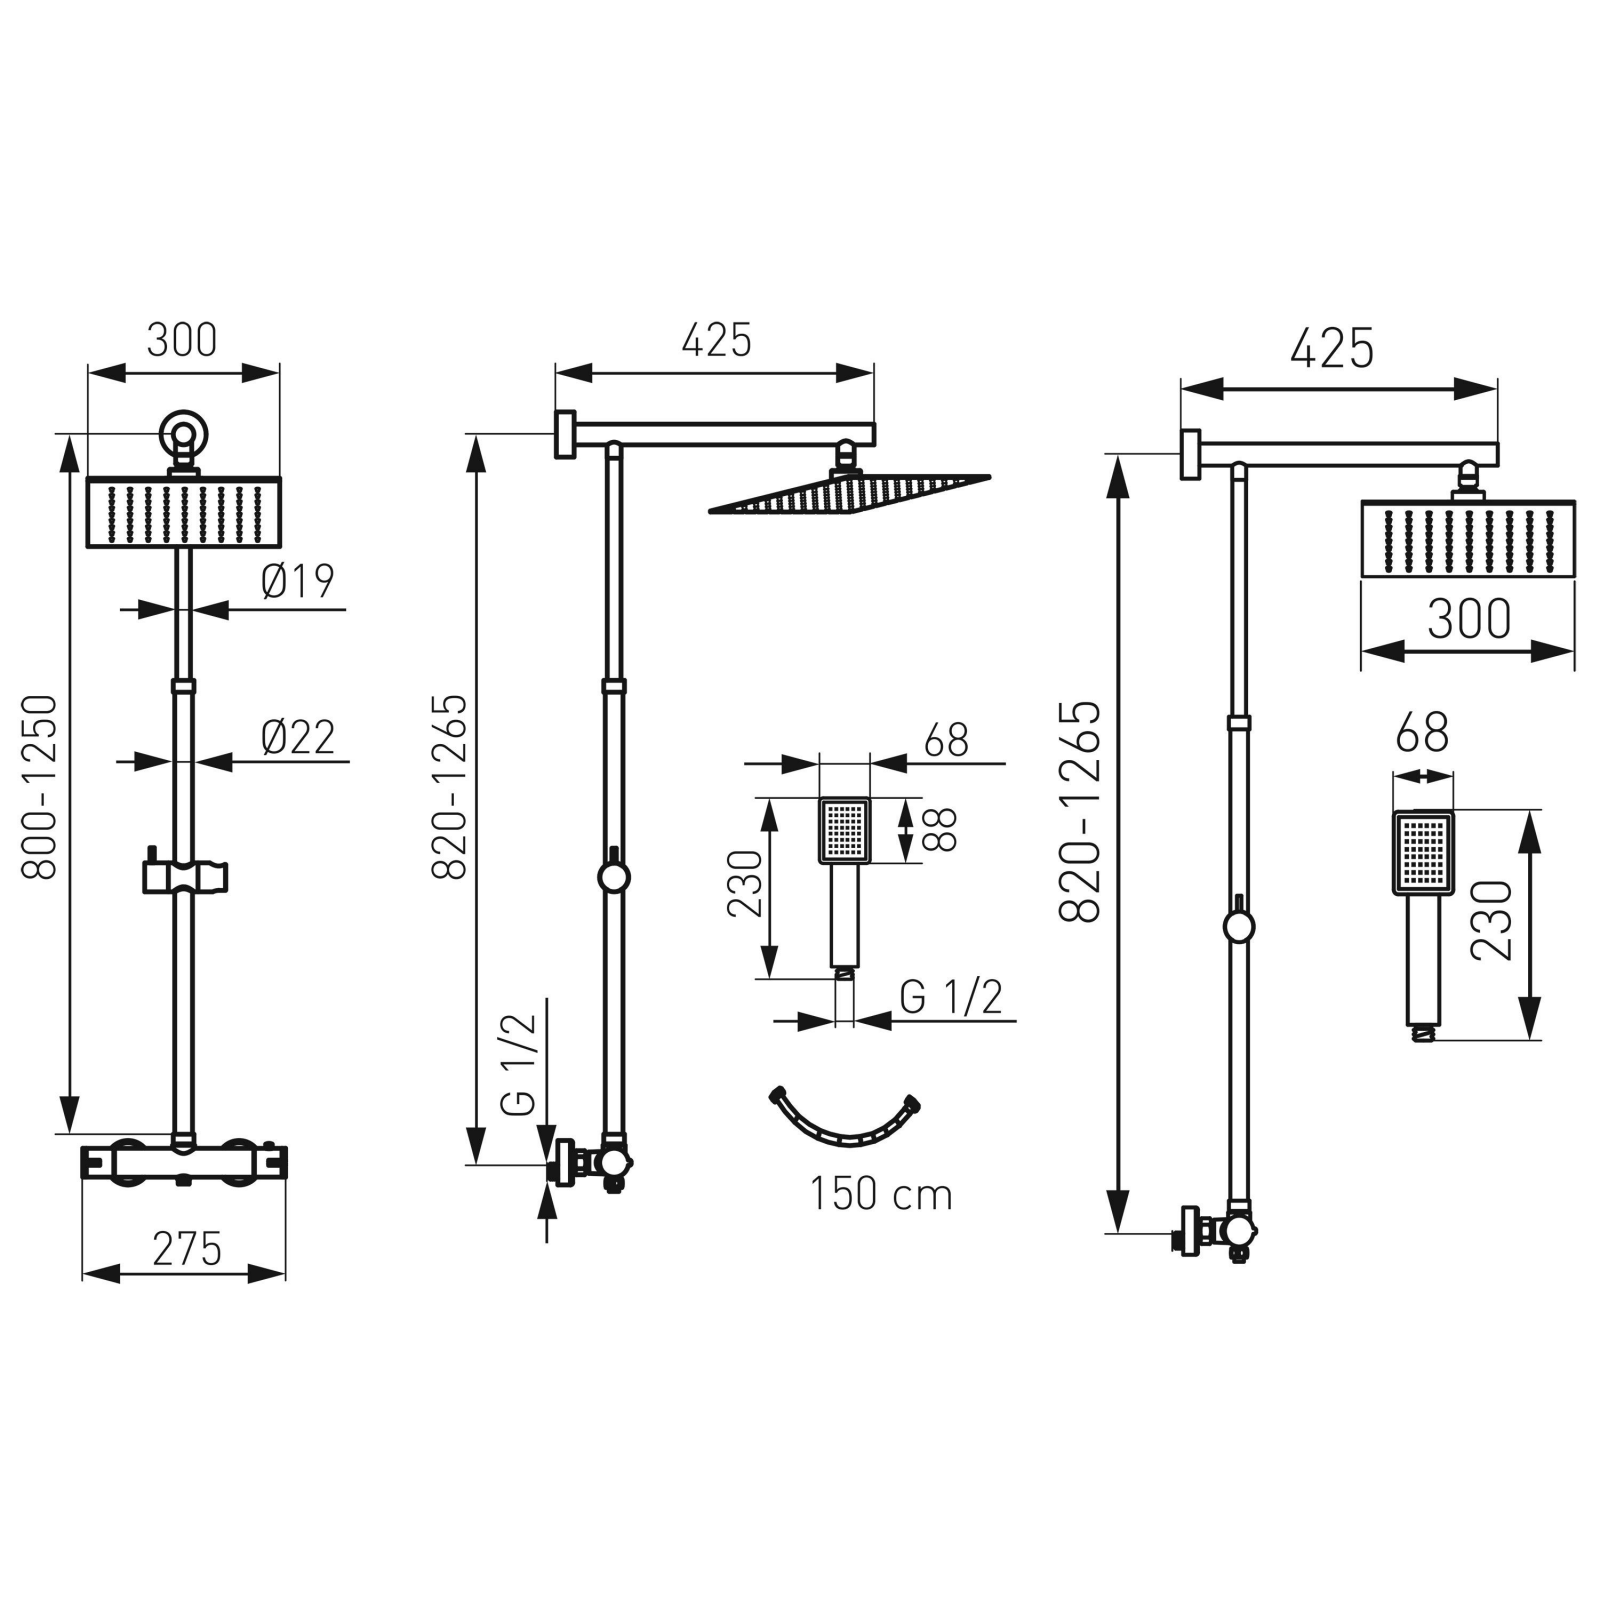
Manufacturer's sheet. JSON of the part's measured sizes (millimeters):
{"part_name": "TREVI New", "step_written_by": "UGS - NX 4.0 (CONFIG_CONTROL_DESIGN)", "units": "millimeters", "bodies": {"solids": 28, "faces": 3511, "planar": 1715, "cylindrical": 836, "other": 960}, "overall_size": [1114.41, 549.97, 365.97], "volume_mm3": 2366000, "surface_area_mm2": 582796, "round_holes": [[1.5, 81], [4.28, 7], [17, 4], [5.5, 3], [20, 3], [22, 3], [28, 3], [58, 3], [25, 2], [25.3, 2], [7, 1], [12, 1]], "round_bosses_or_shafts": [[4.18, 7], [23, 4], [13, 4], [26, 3], [60, 2], [38, 2], [27, 2], [22, 2]], "partial_cylinders_radius": [[0.5, 236], [0.3, 86], [0.75, 8], [4, 8], [5, 8], [1, 6], [0.75, 4], [0.9, 4]], "face_to_face_distances": [15.5, 12, 3.5, 1, 2.7, 5, 24, 2.97, 2.3, 4.2], "hole_center_spacings": [63.73, 142.5, 90.12, 28.5, 57, 40.31, 127.46, 117.51]}
